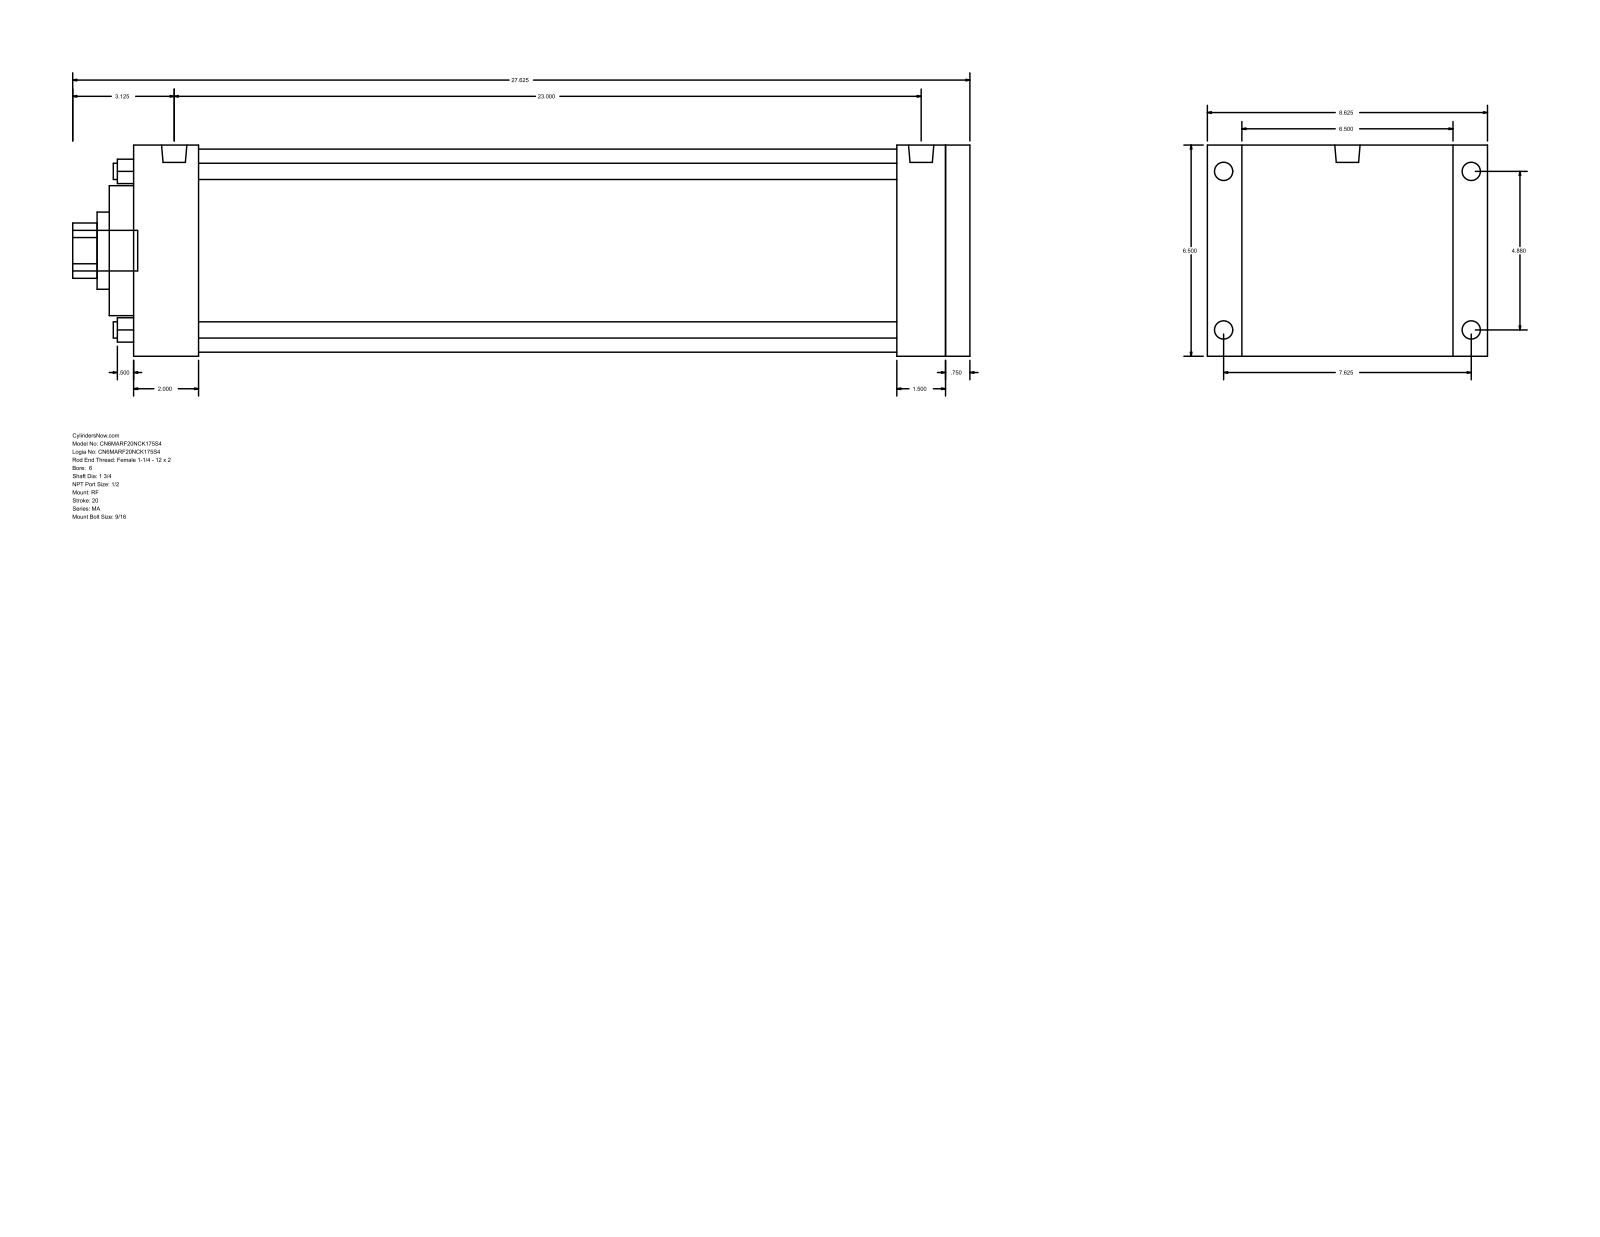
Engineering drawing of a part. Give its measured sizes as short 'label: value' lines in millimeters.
name: MA_RF__0600_1.75
written by: GSSL Pune (CONFIG_CONTROL_DESIGN)
unit: mm
bodies: 0 solids, 94 faces (65 planar, 29 cylindrical, 0 other)
size: 701.67 × 219.07 × 165.1
holes: 4× ⌀12.7, 1× ⌀44.45, 1× ⌀60.33, 1× ⌀101.6, 1× ⌀158.75
bosses: 4× ⌀17.46, 4× ⌀14.29, 2× ⌀19.77, 1× ⌀31.75
rounds: 1× R21.63
face distances: 165.1, 654.05, 19.05, 635, 38.1, 50.8, 584.2, 603.25, 596.9, 546.1
hole spacings: 87.65, 123.96, 175.31
